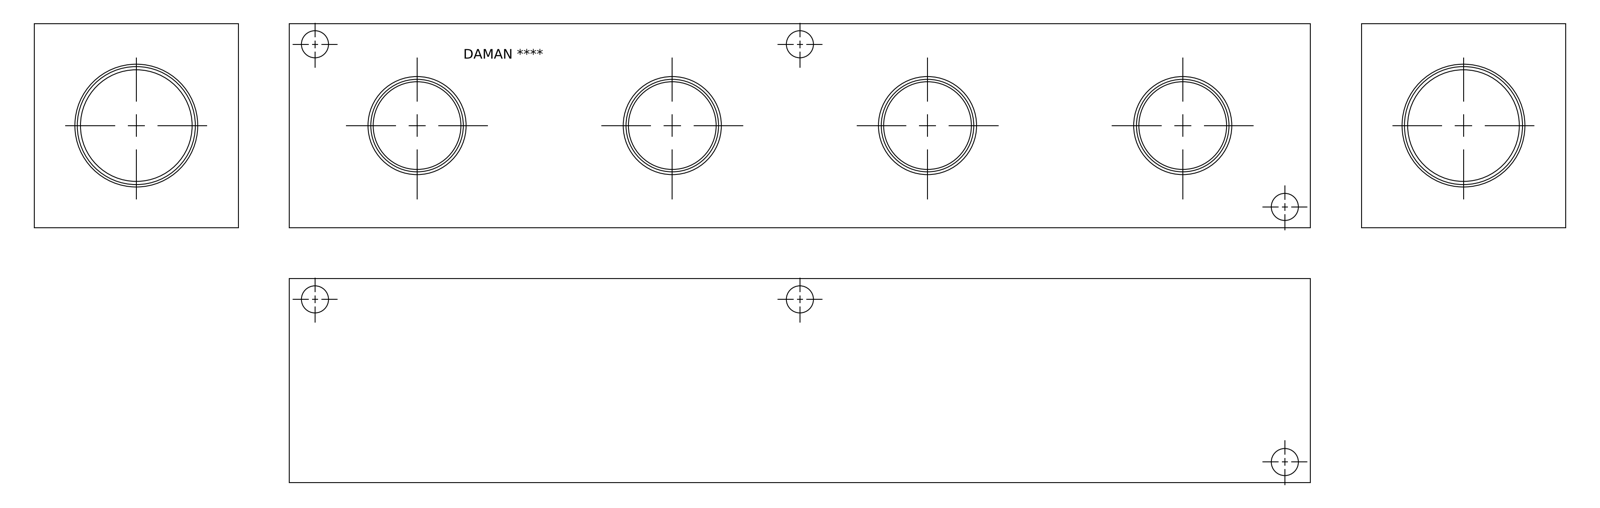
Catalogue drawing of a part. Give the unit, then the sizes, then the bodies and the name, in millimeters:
Units: millimetres
Overall size (bounding box): 508 × 101.6 × 101.6
Round holes (diameter × count): ⌀13.49 ×6, ⌀43.64 ×4, ⌀48.56 ×4, ⌀55.58 ×1, ⌀60.63 ×1
Main face-to-face distances: 101.6, 508, 82.09, 19.51, 19.91, 488.09, 468.18, 101.56, 19.47, 3.62
Hole centre spacings: 127, 64.96, 75.31, 182.35, 194.76, 241.3, 254, 254.53
Volume: 4 913 000 mm³ · Surface area: 250 654 mm²
Bodies: 1 solid, 341 faces (236 planar, 18 cylindrical, 87 other)
Part name (STEP PRODUCT): Part_+H0000424P_3D
STEP written by: Autodesk Inventor 2020 (AUTOMOTIVE_DESIGN)
